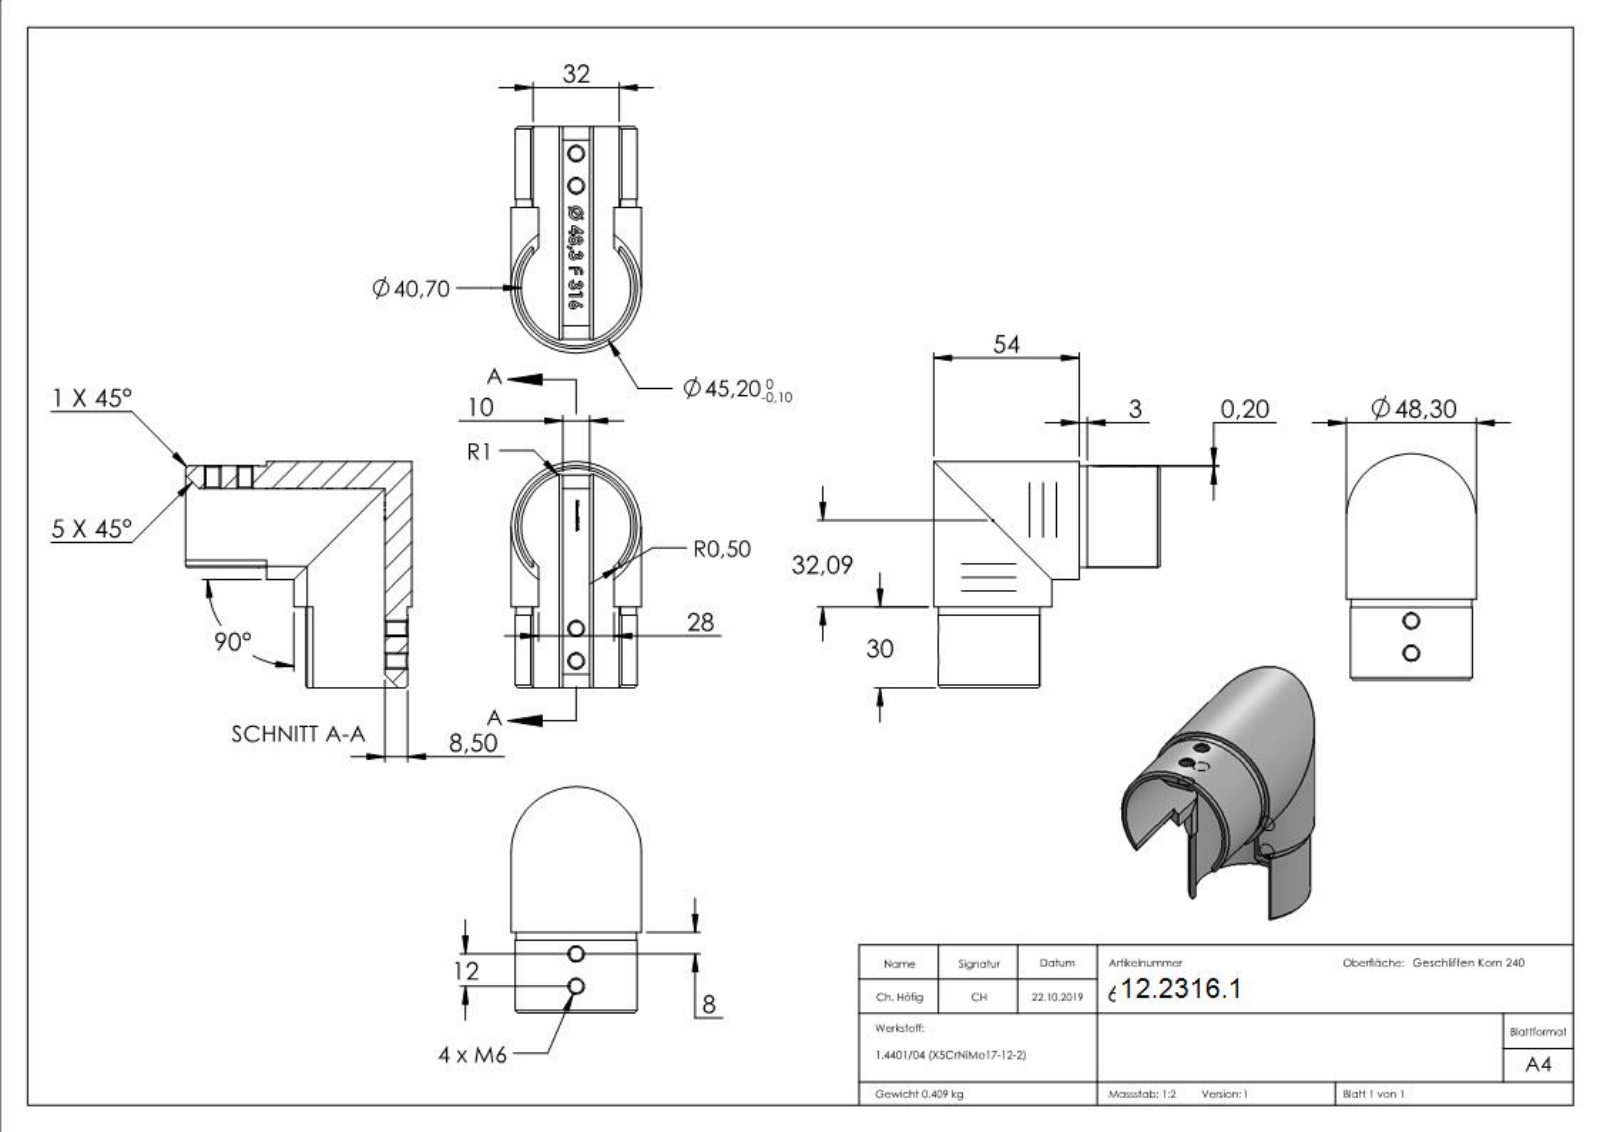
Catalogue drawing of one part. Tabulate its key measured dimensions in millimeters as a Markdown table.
| quantity | value |
| --- | --- |
| part name | 60321-V4A |
| STEP written by | SolidWorks 2015 (CONFIG_CONTROL_DESIGN) |
| units | millimeters |
| bodies | 1 solid, 399 faces (217 planar, 22 cylindrical, 160 other) |
| overall size | 84 × 84 × 48.3 |
| volume | 51 066 mm³ |
| surface area | 30 381 mm² |
| round holes (diameter × count) | 5 × 4 |
| round bosses / shafts (diameter × count) | 48.3 × 2 |
| partial cylindrical surfaces (radius × count) | 0.5 × 4, 1 × 4, 20.35 × 2, 22.4 × 2, 22.6 × 2 |
| main face-to-face distances | 10, 30, 43.95, 73.95, 11, 21, 9, 2, 19, 32 |
| hole center spacings | 12 |
